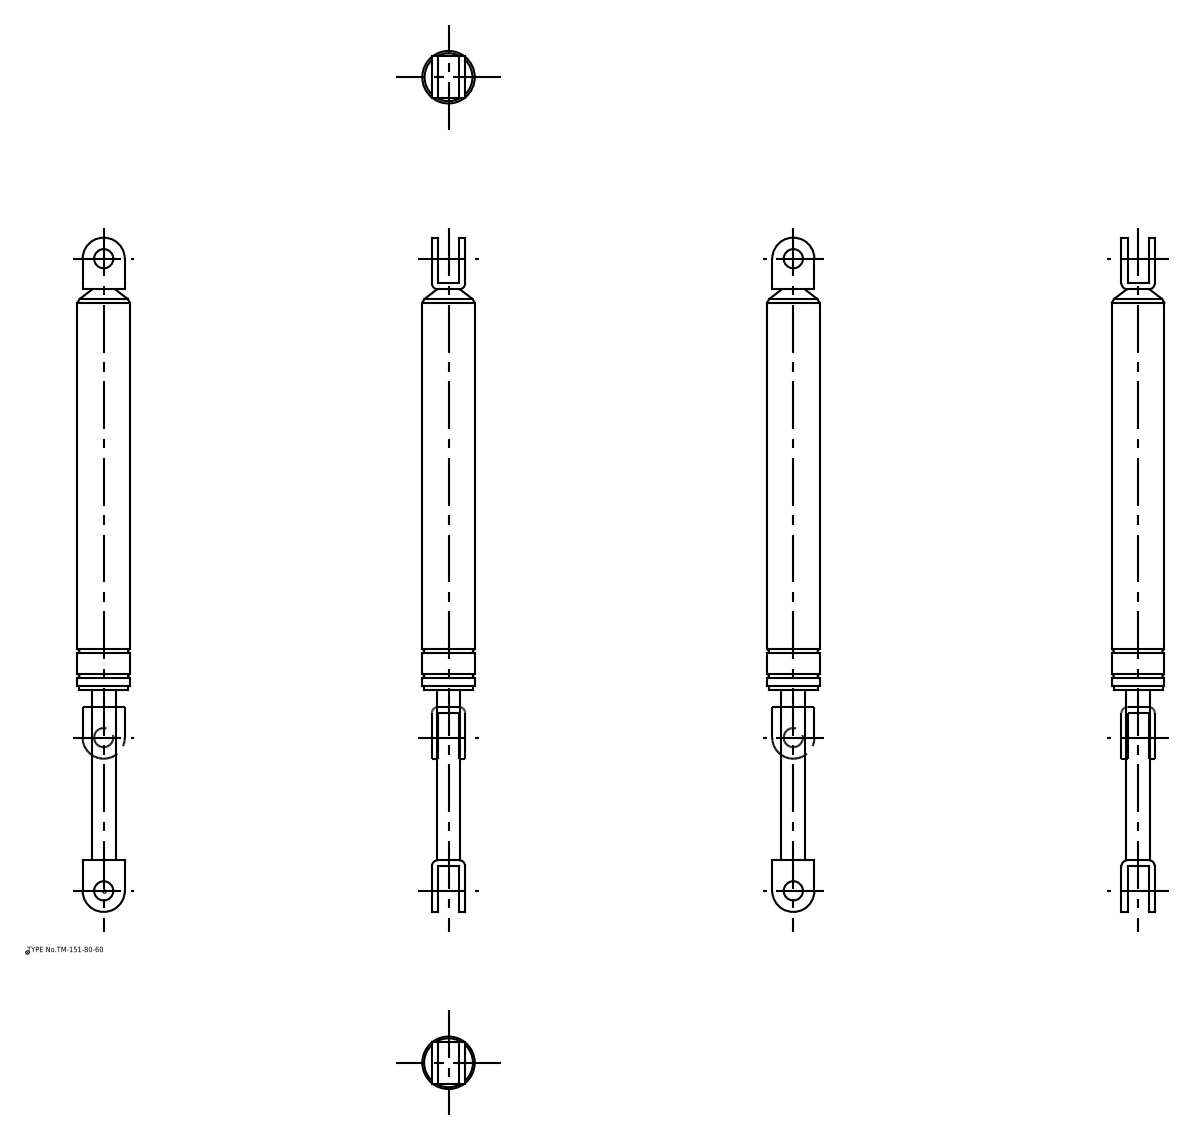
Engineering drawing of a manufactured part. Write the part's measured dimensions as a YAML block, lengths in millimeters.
part_name: "TM_151_80_60; TM_151_80_60_div"
step_written_by: "spGate 16.7.1 (AUTOMOTIVE_DESIGN)"
units: millimeters
bodies: {solids: 2, faces: 64, planar: 22, cylindrical: 32, other: 10}
overall_size: [352, 28.2, 28.2]
volume: 139851
surface_area: 28267
round_holes:
  - {diameter: 10, count: 2}
round_bosses_or_shafts:
  - {diameter: 28.2, count: 1}
  - {diameter: 27.4, count: 1}
  - {diameter: 25.5, count: 1}
  - {diameter: 12.5, count: 1}
partial_cylinders:
  - {radius: 3.2, count: 4}
  - {radius: 11, count: 2}
face_to_face_distances: [3.2, 14.2, 17.4, 11, 22, 301.2, 92.2, 304.4, 212.2, 209]
hole_center_spacings: [330]
